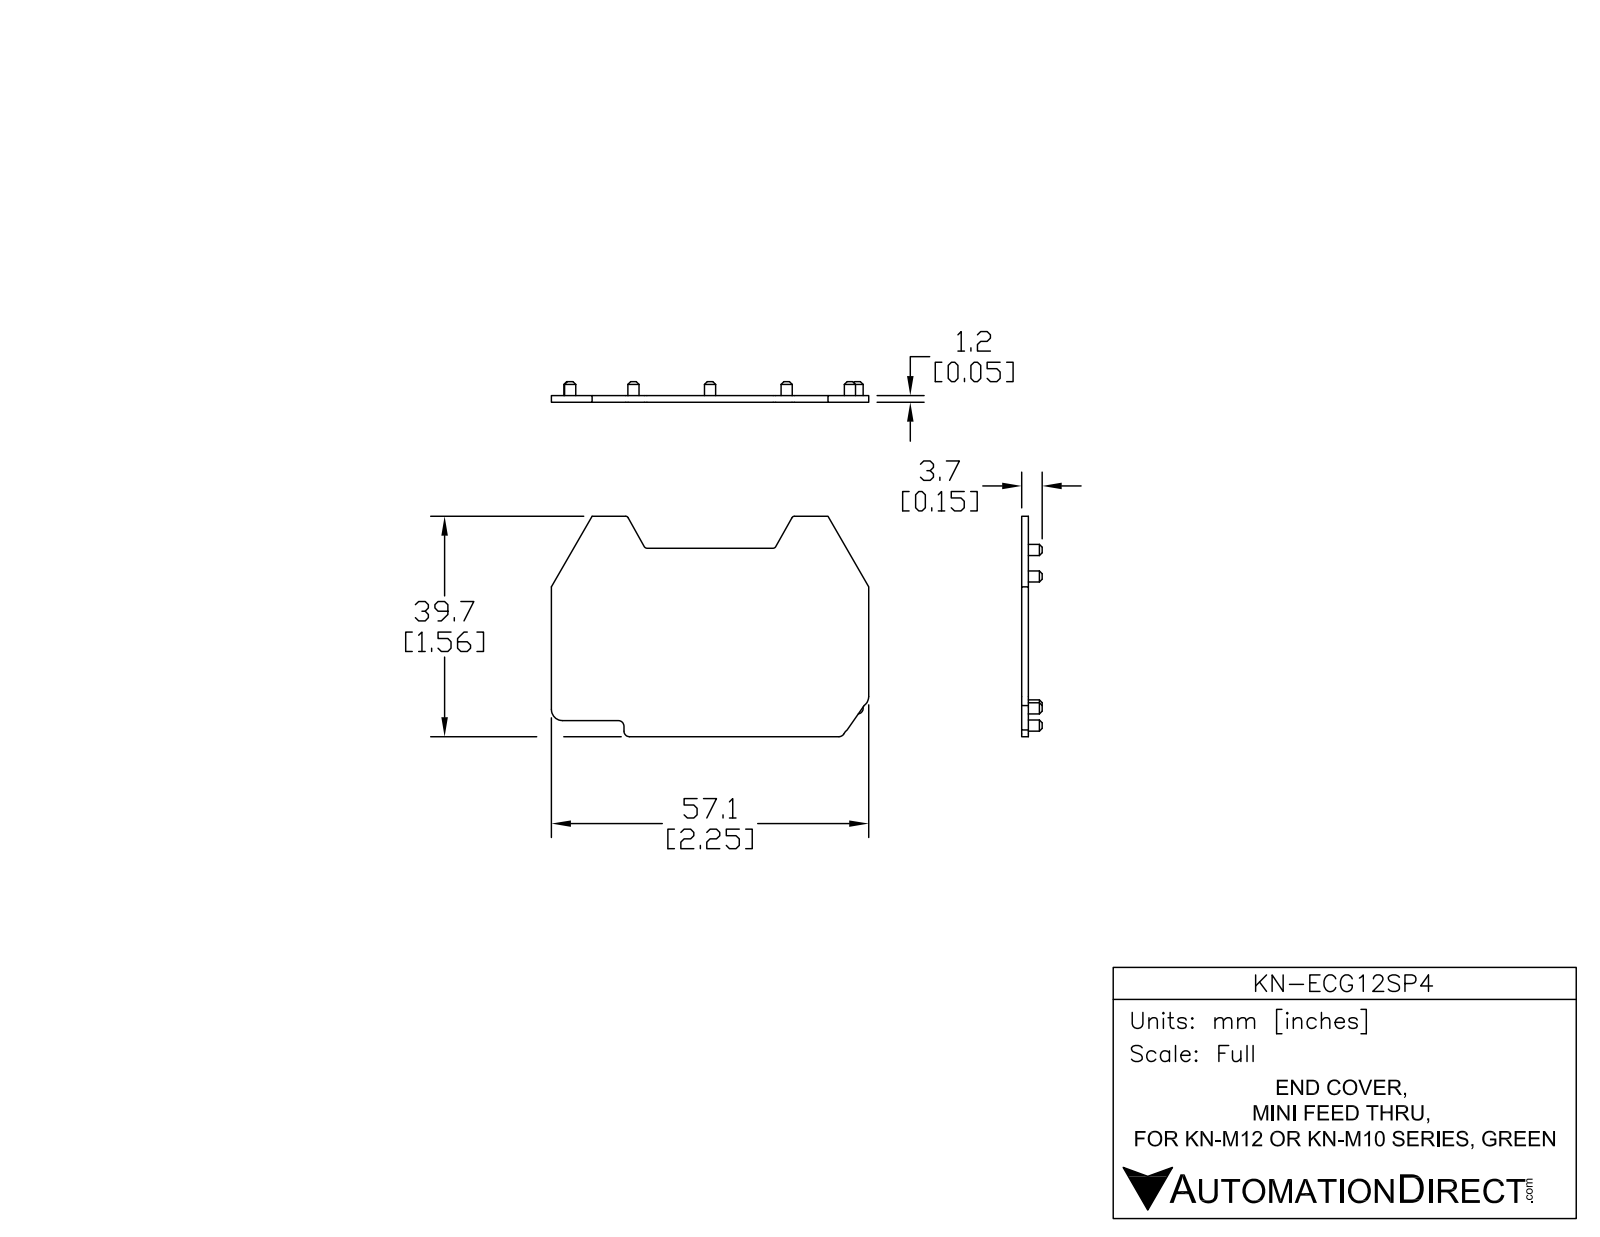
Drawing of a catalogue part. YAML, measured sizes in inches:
part_name: "KN-ECG12SP4"
step_written_by: "SolidWorks 2014 (AUTOMOTIVE_DESIGN)"
units: inches
bodies: {solids: 1, faces: 82, planar: 30, cylindrical: 38, other: 14}
overall_size: [2.248, 1.561, 0.146]
volume: 0.146
surface_area: 6.656
round_holes:
  - {diameter: 0.036, count: 7}
round_bosses_or_shafts:
  - {diameter: 0.079, count: 7}
partial_cylinders:
  - {radius: 0.02, count: 4}
  - {radius: 0.039, count: 3}
  - {radius: 0.079, count: 3}
face_to_face_distances: [0.047, 1.335, 2.248, 1.561, 0.226, 0.114, 1.22, 1.447, 0.514, 1.734]
hole_center_spacings: [0.486, 1.357, 1.448, 1.545, 0.913, 0.935, 1.006, 1.052]
